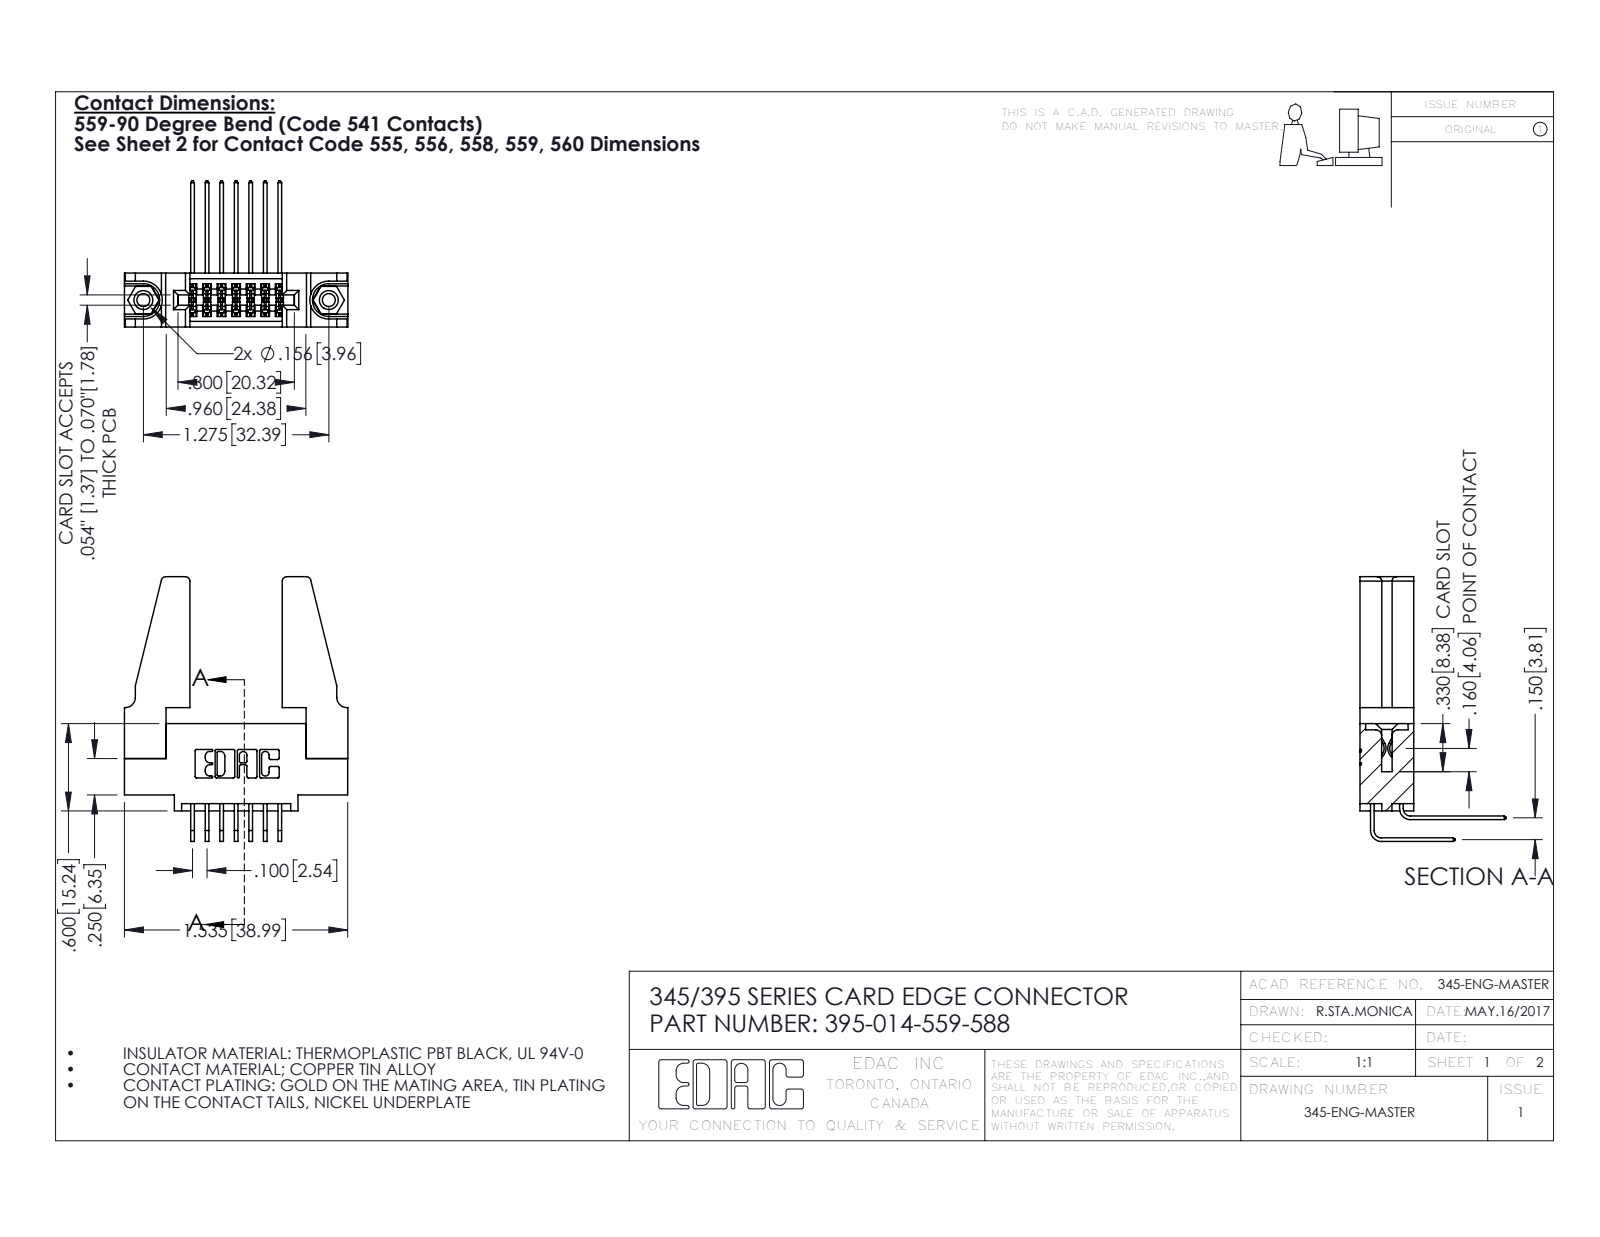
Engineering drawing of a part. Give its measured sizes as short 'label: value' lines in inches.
name: 345-220-078_345-220-088; 345-292-001_558 559 Tail - 1; 395-014-559-588; 345-292-001_559 Tail - 2 (+2 more)
written by: SolidWorks 2016 (CONFIG_CONTROL_DESIGN)
unit: in
bodies: 19 solids, 982 faces (646 planar, 320 cylindrical, 16 other)
size: 1.819 × 1.536 × 1.005
volume: 0.41 in³; area: 12.48 in²
holes: 2× ⌀0.089, 2× ⌀0.125, 2× ⌀0.156, 1× ⌀0.064
bosses: 2× ⌀0.155
rounds: 22× R0.006, 22× R0.01, 8× R0.03, 6× R0.007, 6× R0.031, 3× R0.026, 2× R0.014, 2× R0.019
face distances: 0.37, 0.072, 0.298, 0.2, 0.098, 0.272, 0.025, 0.225, 0.15, 0.148
hole spacings: 0.27, 1.045, 1.275
